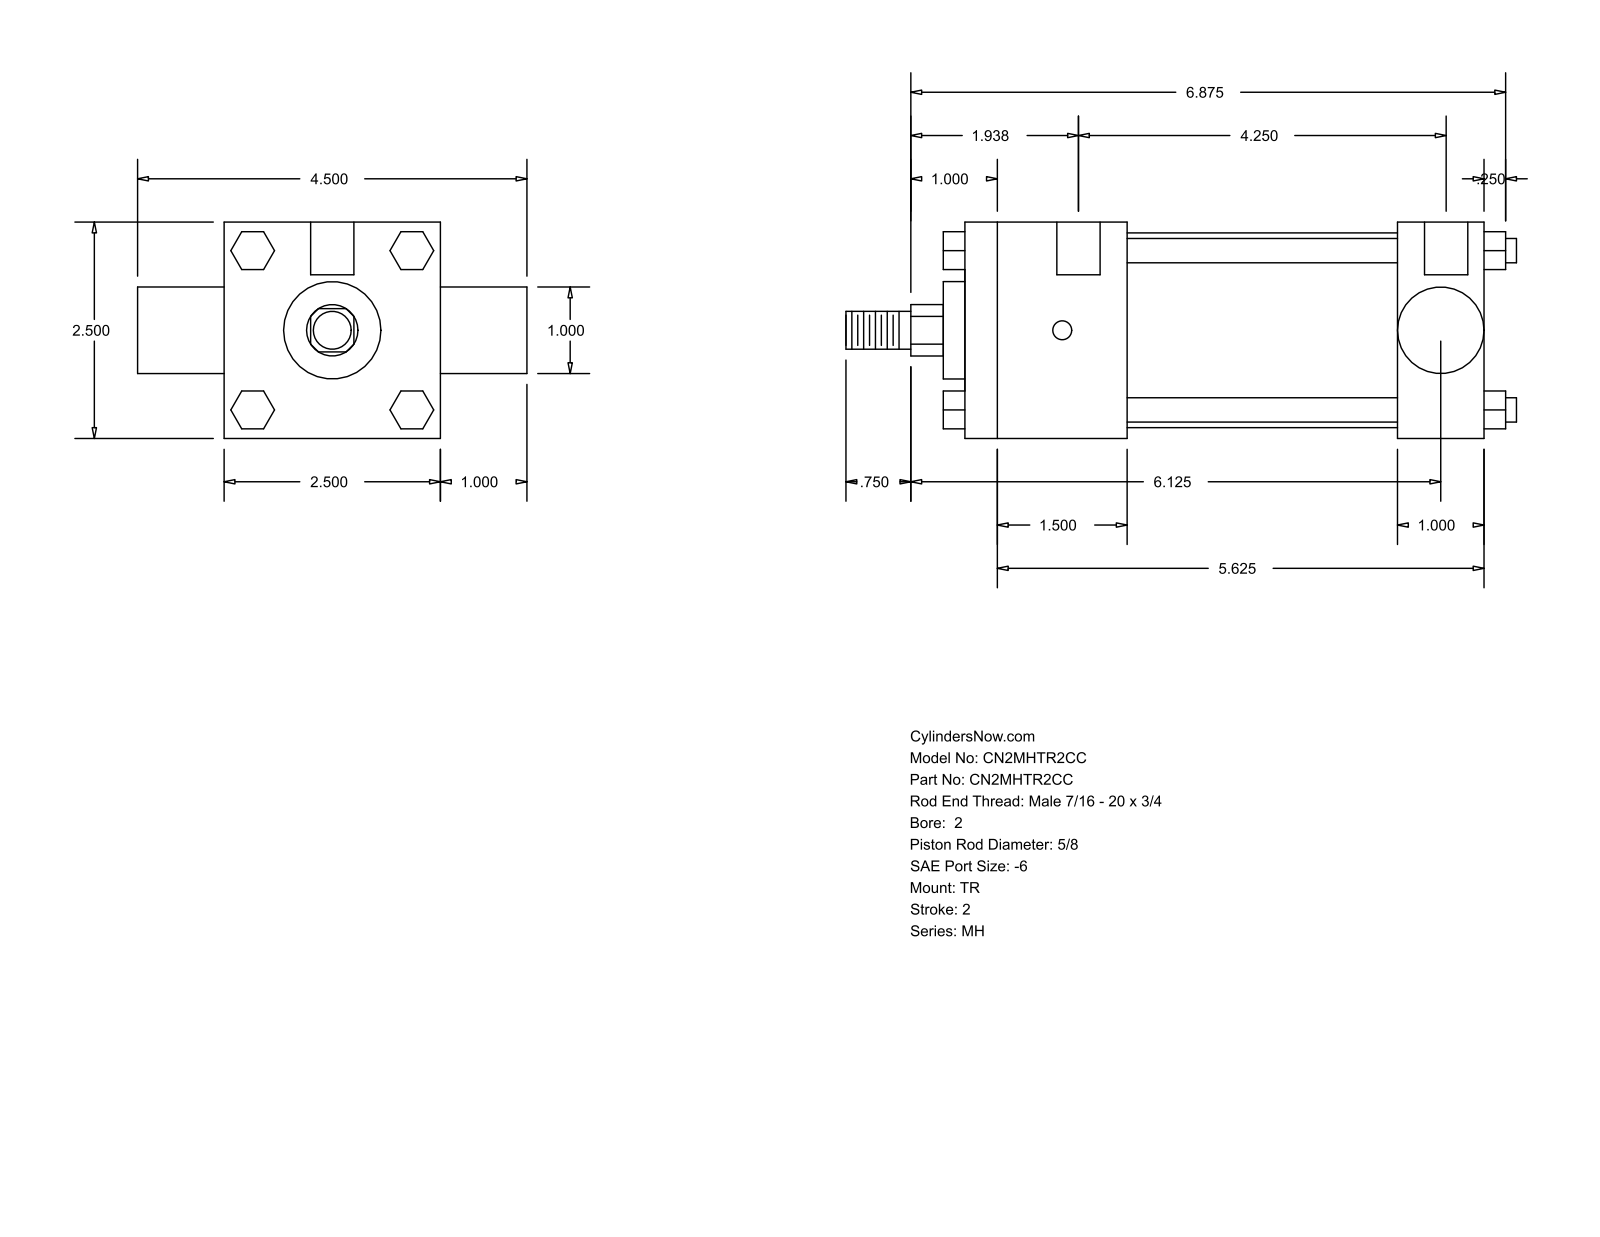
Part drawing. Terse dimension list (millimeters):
name: MH_TR__0200_0.625
written by: GSSL Pune (CONFIG_CONTROL_DESIGN)
unit: mm
bodies: 0 solids, 120 faces (92 planar, 28 cylindrical, 0 other)
size: 196.85 × 114.3 × 63.5
holes: 3× ⌀5.56, 2× ⌀12.7
bosses: 4× ⌀7.14, 1× ⌀57.15, 1× ⌀28.57, 1× ⌀25.35, 1× ⌀15.88, 1× ⌀11.11
rounds: 1× R7.54
face distances: 63.5, 152.4, 25.4, 47.62, 127, 79.38, 104.78, 88.9, 6.35, 53.97
hole spacings: 3.18, 4.76, 107.95, 111.13, 112.71, 115.89
